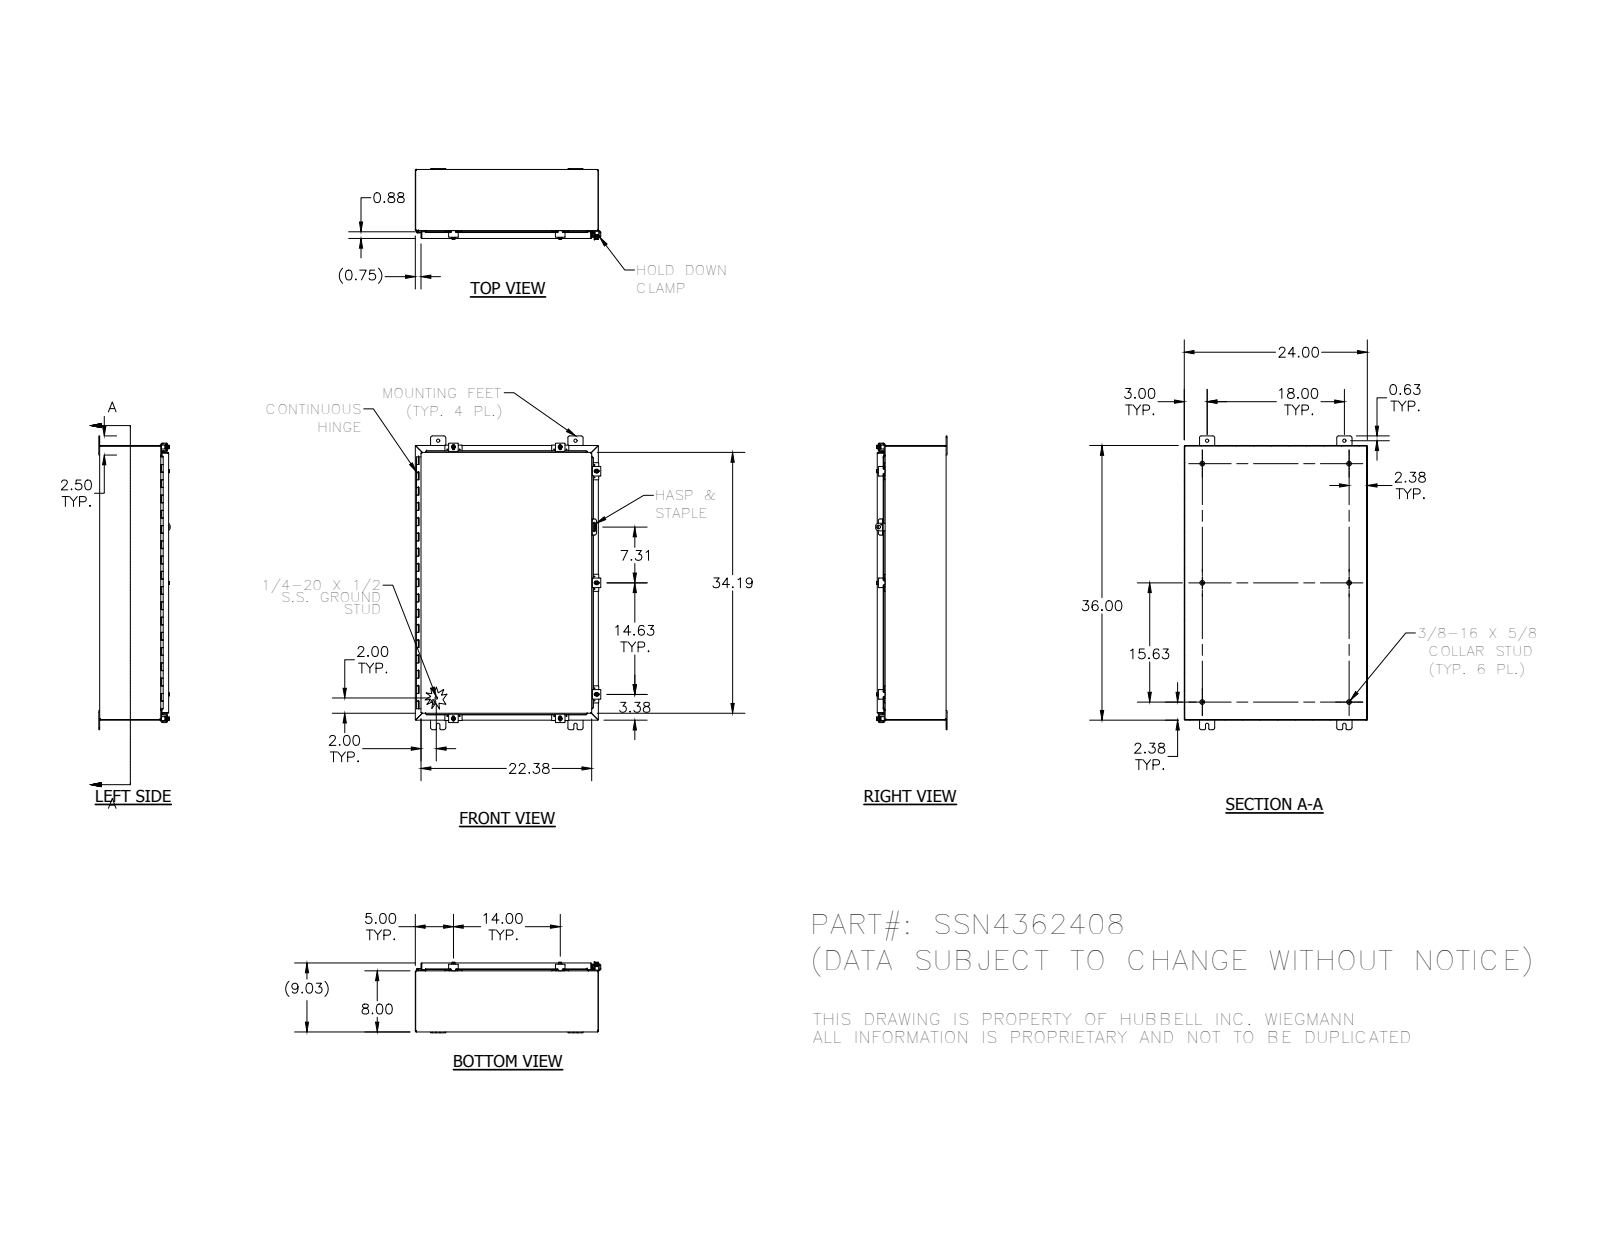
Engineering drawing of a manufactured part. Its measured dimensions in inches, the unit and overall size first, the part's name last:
Units: inches
Overall size (bounding box): 38.5 × 24.311 × 9.355
Round holes (diameter × count): ⌀0.11 ×14, ⌀0.211 ×7, ⌀0.281 ×7, ⌀0.3 ×7, ⌀0.438 ×4, ⌀0.125 ×1, ⌀0.156 ×1, ⌀0.5 ×1
Round bosses / shafts (diameter × count): ⌀0.25 ×9, ⌀0.52 ×7, ⌀0.5 ×7, ⌀0.35 ×7, ⌀0.625 ×6, ⌀0.33 ×6, ⌀0.115 ×2, ⌀0.337 ×1
Partial cylindrical surfaces — rounded edges, fillets, slot ends (radius × count): R0.03 ×83, R0.125 ×37, R0.25 ×33, R0.031 ×23, R0.105 ×23, R0.062 ×15, R0.141 ×14, R0.1 ×10
Main face-to-face distances: 0.074, 8.959, 8.885, 9.033, 23.926, 35.926, 7.926, 1.033, 23.852, 24
Hole centre spacings: 0.876, 35.298, 14, 1.625, 13.191, 14.816, 34.961, 34.998
Volume: 241 in³ · Surface area: 6 344 in²
Bodies: 54 solids, 2204 faces (846 planar, 983 cylindrical, 375 other)
Part name (STEP PRODUCT): 30818; HFW30825-4; 38412; 34871 (+8 more)
STEP written by: SolidWorks 2014 (AUTOMOTIVE_DESIGN)
